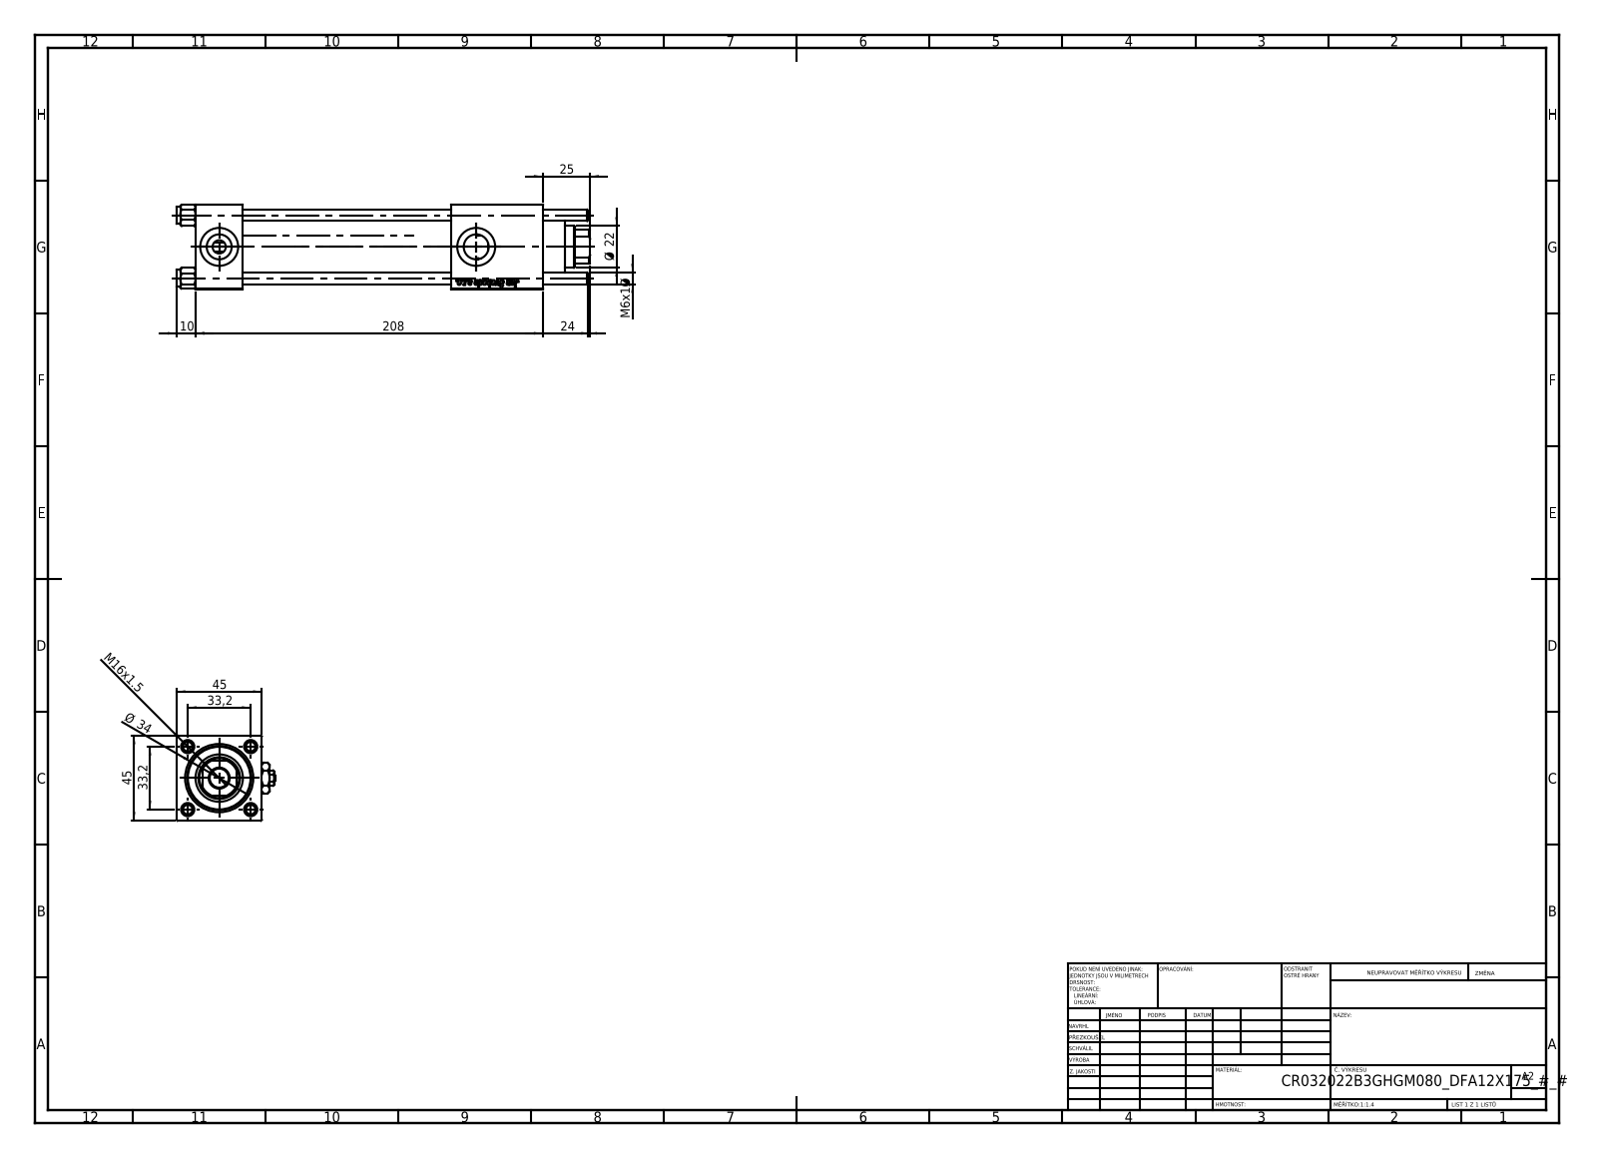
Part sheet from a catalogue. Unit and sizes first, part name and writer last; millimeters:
Units: millimetres
Overall size (bounding box): 218 × 52 × 45
Round holes (diameter × count): ⌀6 ×4, ⌀7 ×2, ⌀13.16 ×2, ⌀20 ×2, ⌀10.5 ×1, ⌀22 ×1, ⌀24 ×1, ⌀25 ×1, ⌀32 ×1, ⌀33 ×1
Round bosses / shafts (diameter × count): ⌀9 ×4, ⌀38 ×1, ⌀34 ×1, ⌀28 ×1, ⌀12 ×1, ⌀10 ×1
Partial cylindrical surfaces — rounded edges, fillets, slot ends (radius × count): R9.75 ×1, R10.5 ×1
Main face-to-face distances: 45, 25, 135, 183, 110, 158, 44.8, 48, 13, 154.3
Hole centre spacings: 23.48, 33.2, 46.95, 135.5
Volume: 271 979 mm³ · Surface area: 104 919 mm²
Bodies: 14 solids, 1289 faces (490 planar, 97 cylindrical, 702 other)
Part name (STEP PRODUCT): V215CR_B_TYCINKA; Zatka_pro_OIL_PORT; V215CR_VCP_B; V215_VC_A (+3 more)
STEP written by: SolidWorks 2019 (CONFIG_CONTROL_DESIGN)
